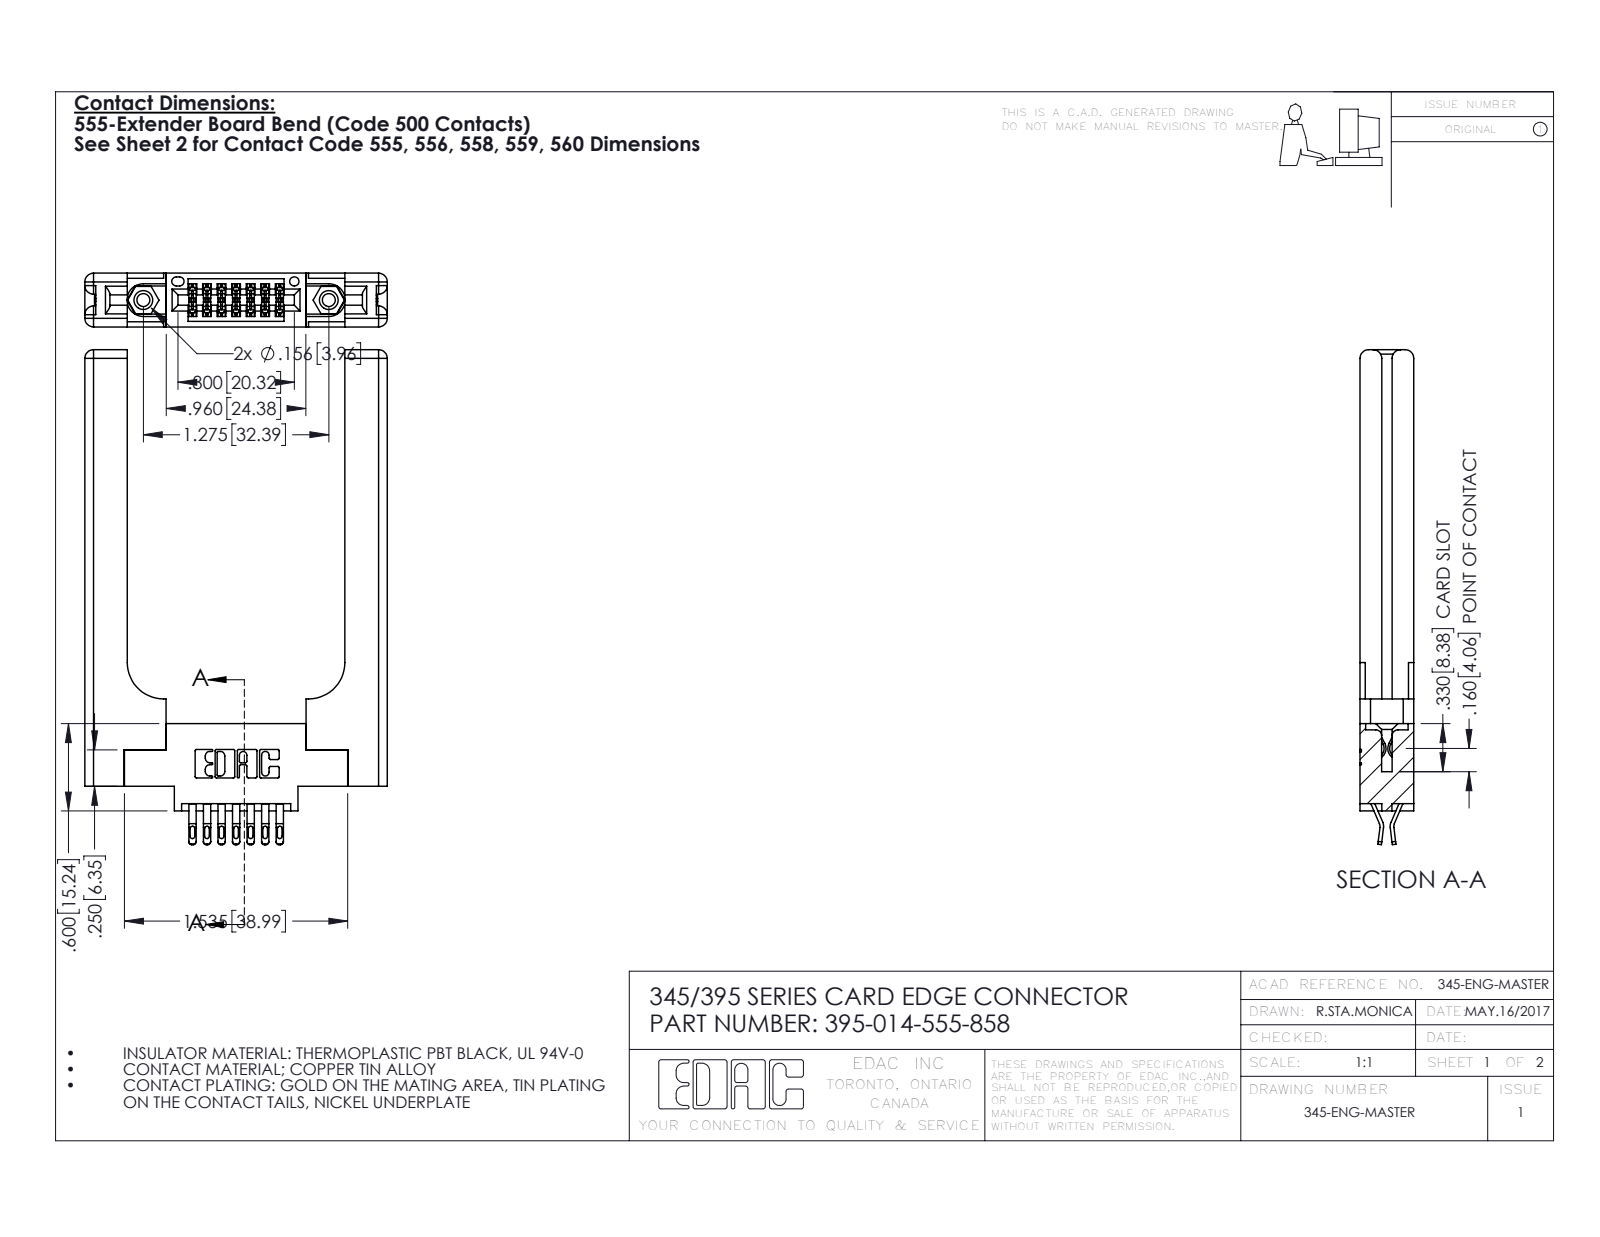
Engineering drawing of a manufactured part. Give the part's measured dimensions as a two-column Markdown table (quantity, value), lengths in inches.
| quantity | value |
| --- | --- |
| part name | 345-220-058_345-220-058; 345 Part_0.170 Offset - 0.156 Dia-TH; 345-292-001_555 Tail; 395-014-555-858 (+1 more) |
| STEP written by | SolidWorks 2016 (CONFIG_CONTROL_DESIGN) |
| units | inches |
| bodies | 19 solids, 1170 faces (666 planar, 444 cylindrical, 60 other) |
| overall size | 3.402 × 2.079 × 0.37 |
| volume | 0.806 in³ |
| surface area | 18.07 in² |
| round holes (diameter × count) | 0.089 × 2, 0.125 × 2, 0.156 × 2, 0.064 × 1 |
| round bosses / shafts (diameter × count) | 0.155 × 2 |
| partial cylindrical surfaces (radius × count) | 0.016 × 35, 0.02 × 28, 0.01 × 22, 0.006 × 21, 0.06 × 16, 0.007 × 6, 0.031 × 6, 0.026 × 3 |
| main face-to-face distances | 0.37, 0.15, 0.22, 0.072, 0.148, 0.077, 0.298, 1.496, 0.071, 0.12 |
| hole center spacings | 0.27, 1.045, 1.275 |
